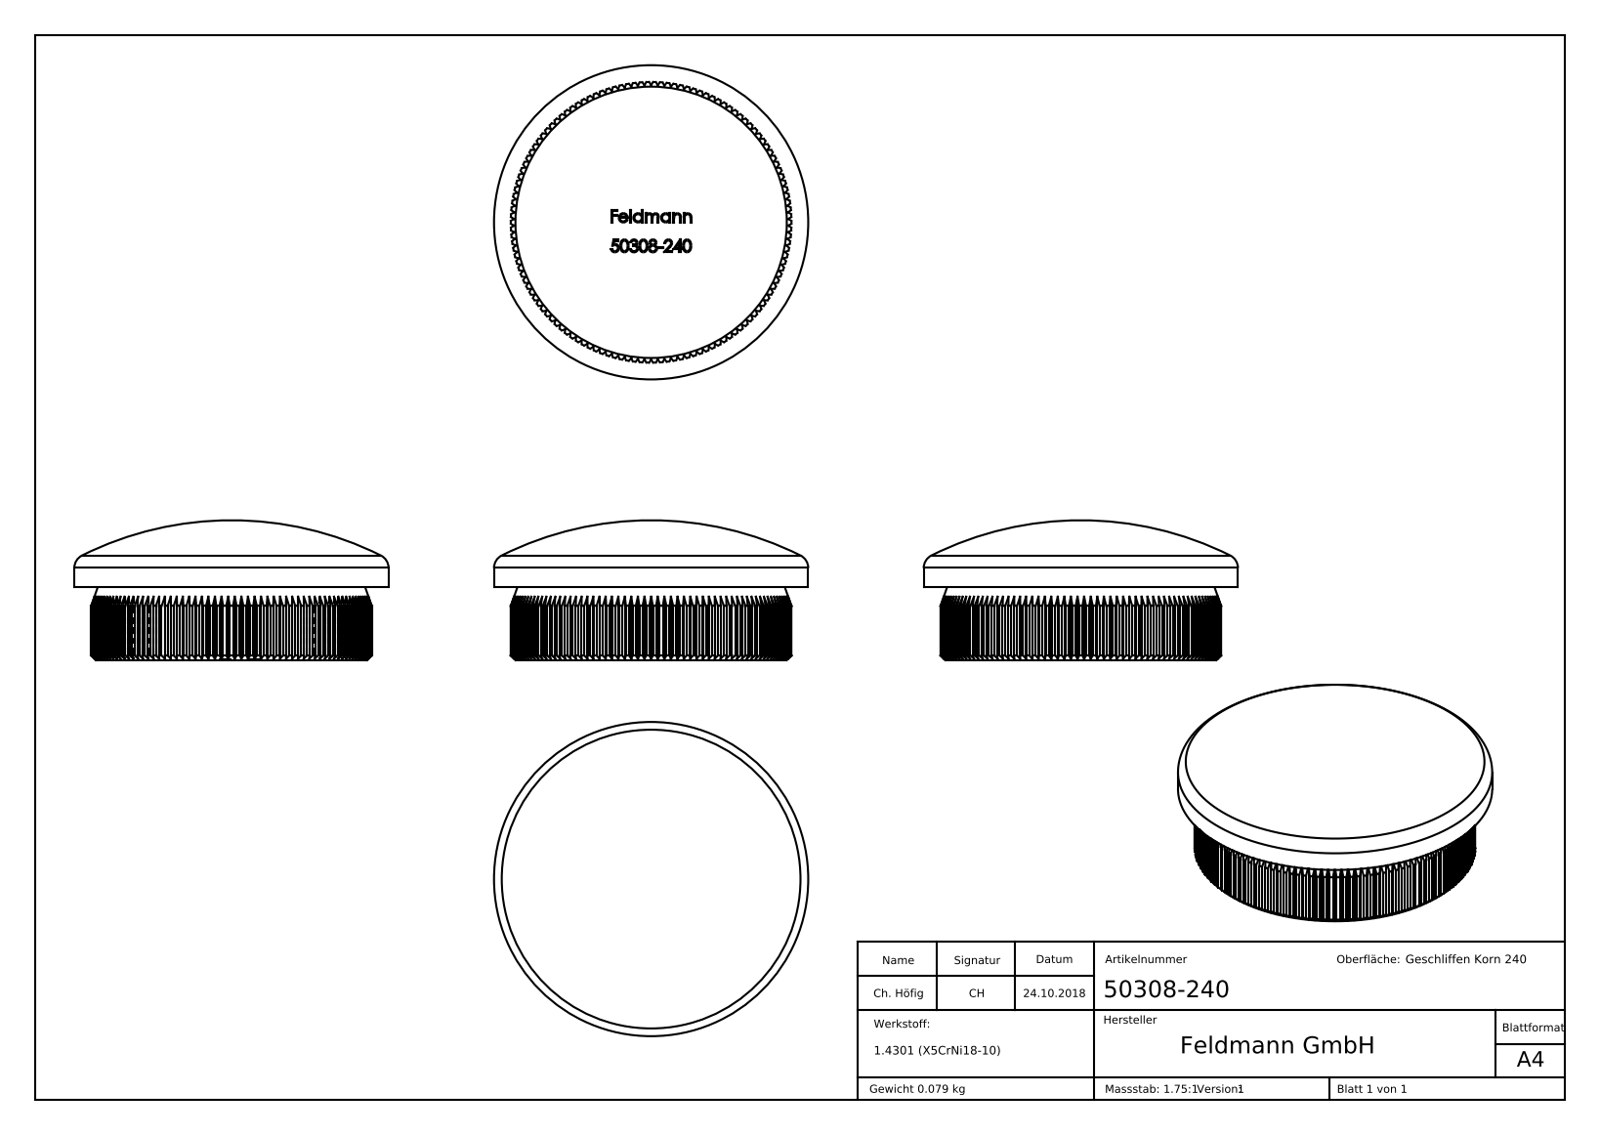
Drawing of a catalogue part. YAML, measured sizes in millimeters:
part_name: "50308-240"
step_written_by: "SolidWorks 2015 (CONFIG_CONTROL_DESIGN)"
units: millimeters
bodies: {solids: 1, faces: 624, planar: 381, cylindrical: 132, other: 111}
overall_size: [33.7, 33.7, 15]
volume: 9993
surface_area: 3234
round_bosses_or_shafts:
  - {diameter: 33.7, count: 1}
partial_cylinders:
  - {radius: 15.05, count: 1}
face_to_face_distances: [7.8, 14.7, 14.72, 14.68, 7.7, 2.97, 0.39, 1.4, 3.39, 3.19]
